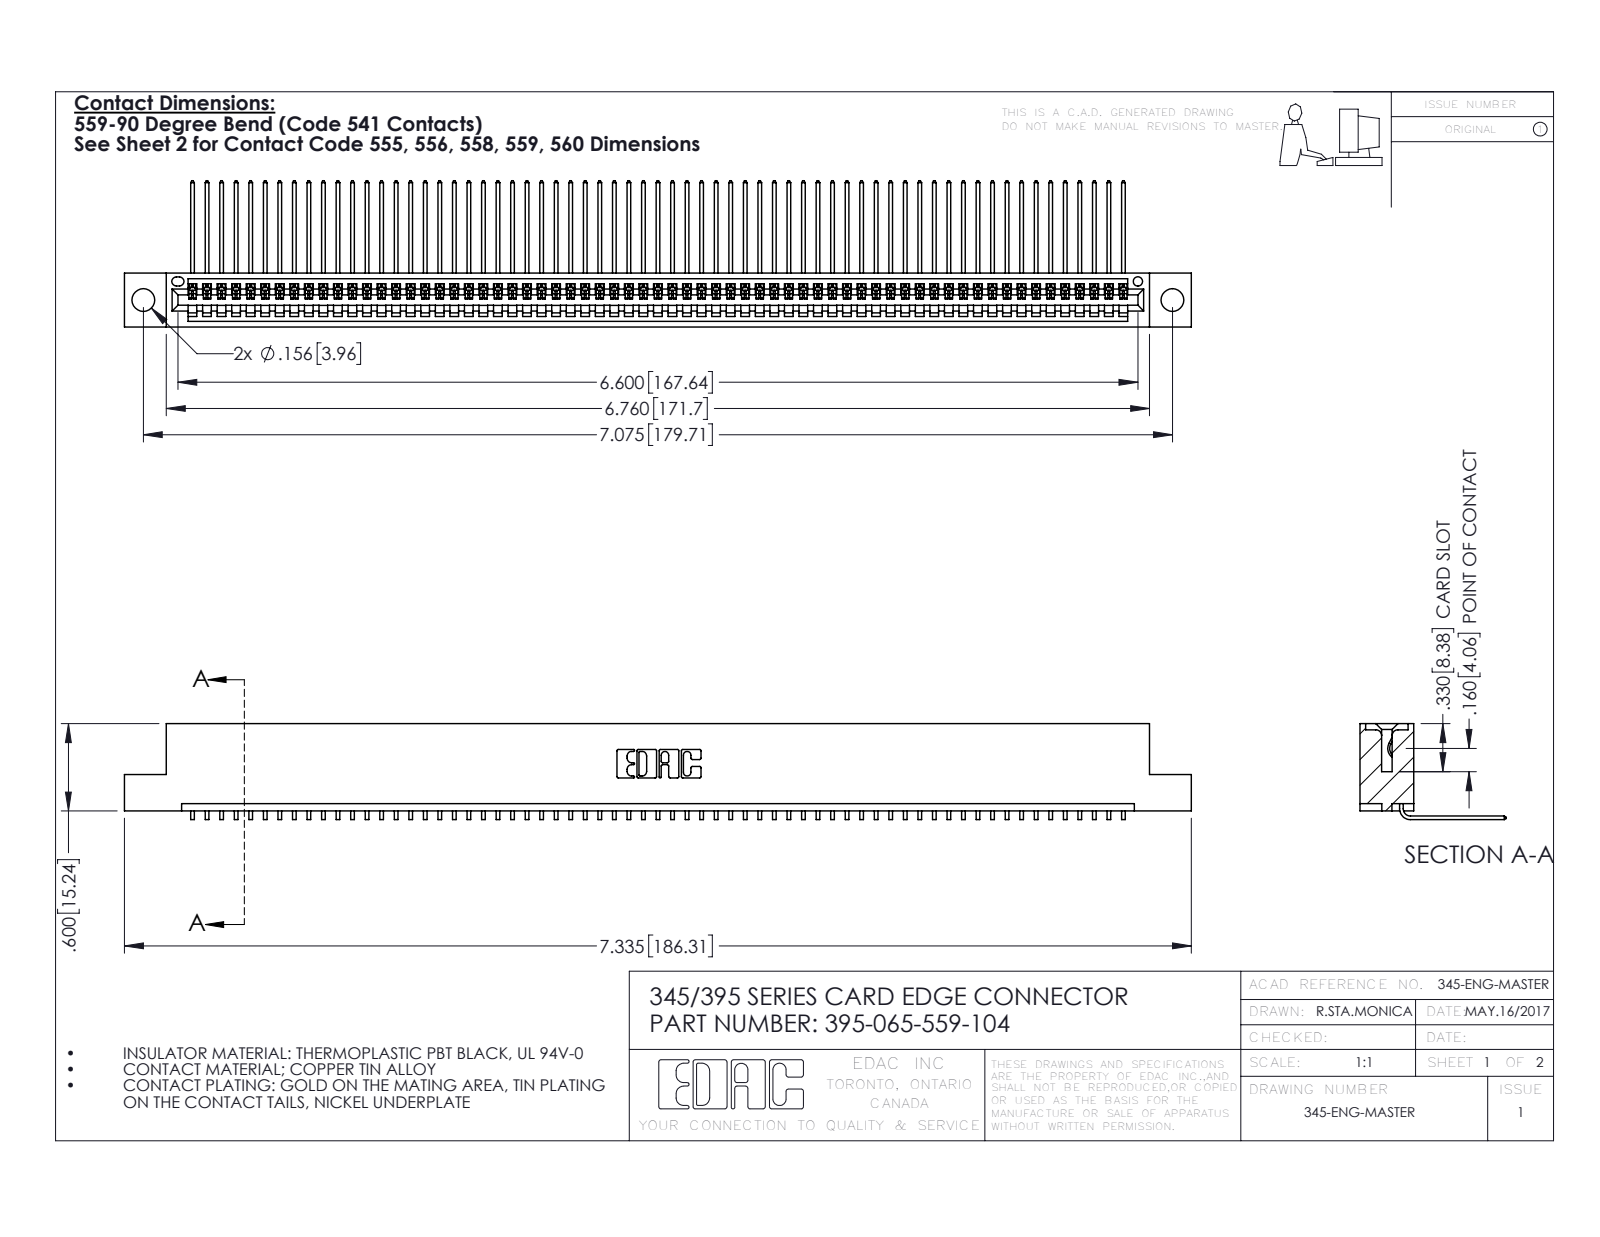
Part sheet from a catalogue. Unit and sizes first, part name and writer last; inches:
Units: inches
Overall size (bounding box): 7.335 × 1.005 × 0.659
Round holes (diameter × count): ⌀0.156 ×2, ⌀0.064 ×1
Partial cylindrical surfaces — rounded edges, fillets, slot ends (radius × count): R0.006 ×130, R0.01 ×22, R0.007 ×6, R0.031 ×6, R0.026 ×3, R0.031 ×2, R0.04 ×2, R0.014 ×1
Main face-to-face distances: 0.298, 0.072, 0.37, 0.2, 0.098, 0.272, 0.025, 0.225, 0.149, 0.072
Hole centre spacings: 0.27, 6.839, 7.075
Volume: 1.099 in³ · Surface area: 39.26 in²
Bodies: 66 solids, 4026 faces (2810 planar, 1216 cylindrical, 0 other)
Part name (STEP PRODUCT): 345-292-001_558 559 Tail - 1; 395-065-559-104; 345 Part_Flush Mounting Lugs - 0.156 Dia-TH
STEP written by: SolidWorks 2016 (CONFIG_CONTROL_DESIGN)
